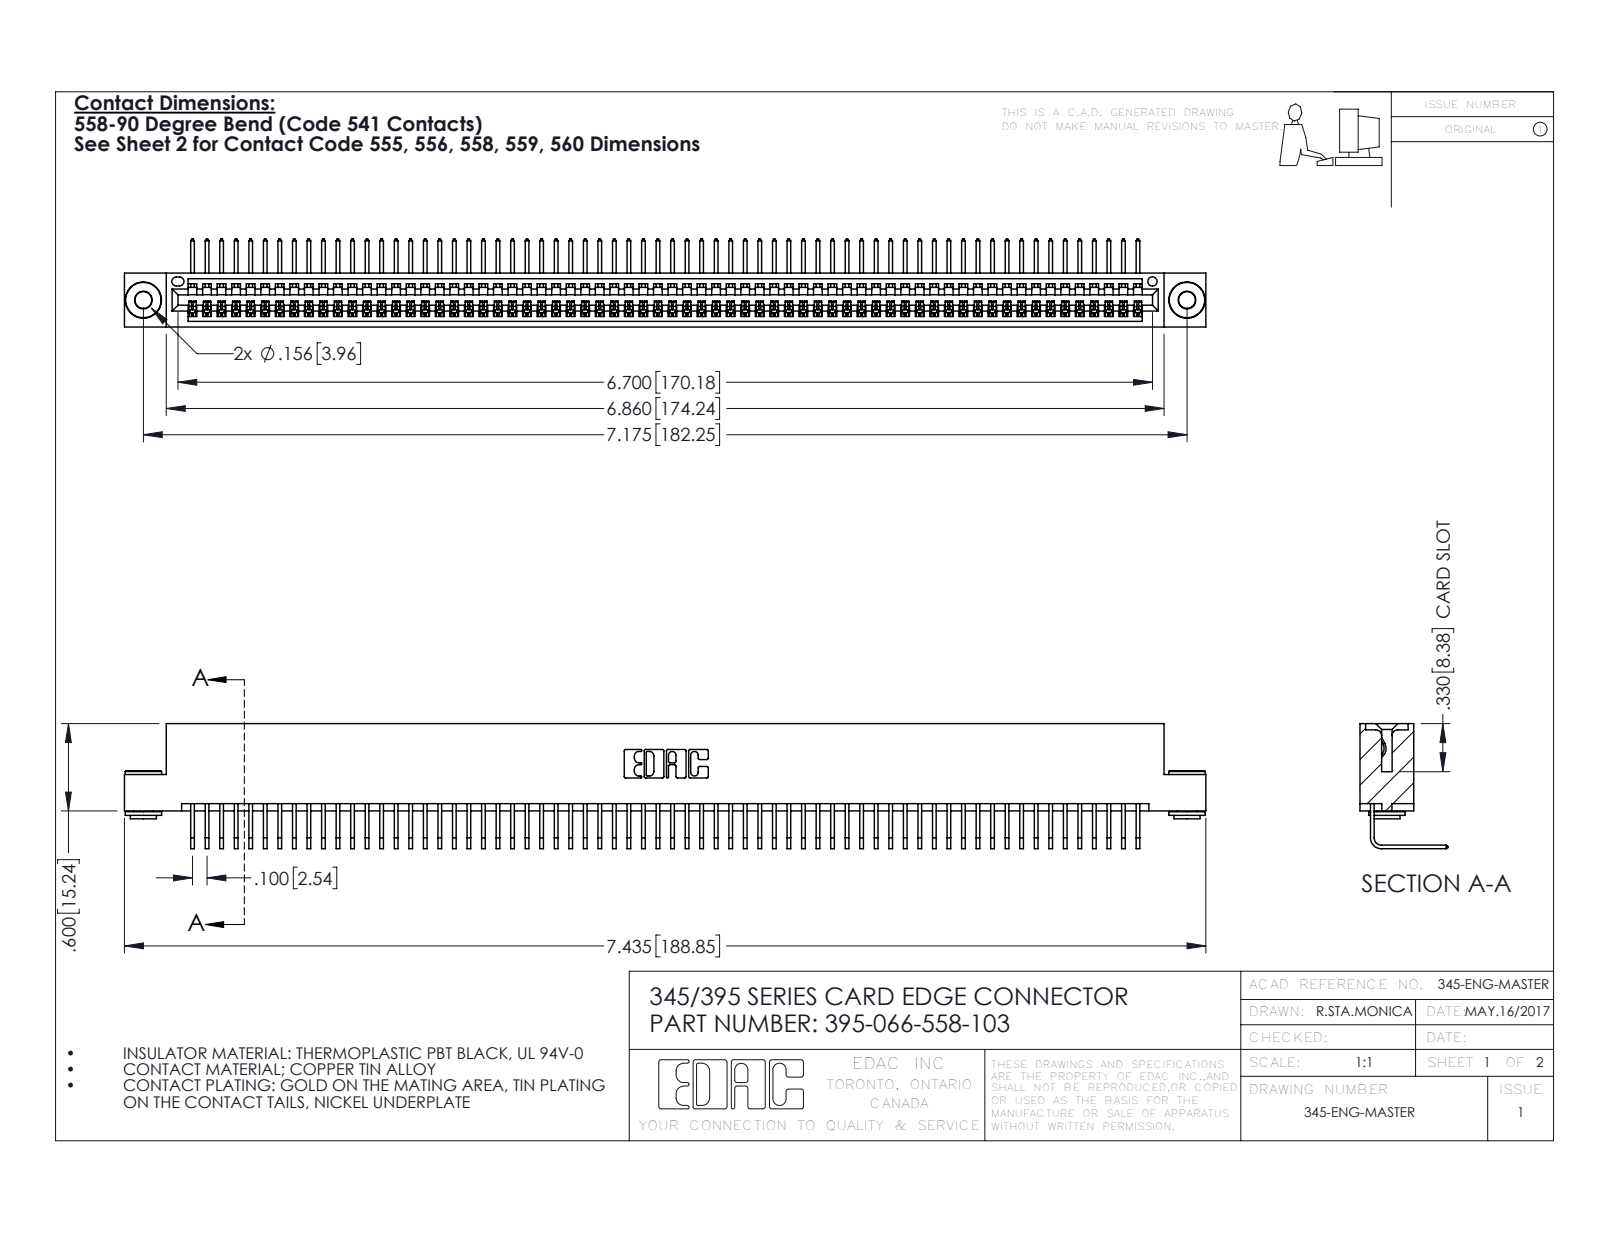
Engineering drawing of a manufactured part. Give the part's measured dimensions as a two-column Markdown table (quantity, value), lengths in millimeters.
| quantity | value |
| --- | --- |
| part name | 345 Part_Flush Mounting Lugs - 0.156 Dia-TH; 345-250-002_345-250-002-102; 345-292-001_558 Tail - 2; 395-066-558-103 |
| STEP written by | SolidWorks 2016 (CONFIG_CONTROL_DESIGN) |
| units | millimeters |
| bodies | 69 solids, 4124 faces (2862 planar, 1254 cylindrical, 8 other) |
| overall size | 188.8 × 21.8 × 15.4 |
| volume | 18 370 mm³ |
| surface area | 26 250 mm² |
| round holes (diameter × count) | 2.9 × 2, 4 × 2, 1.6 × 1 |
| round bosses / shafts (diameter × count) | 6.4 × 2, 4.6 × 2, 3.5 × 2 |
| partial cylindrical surfaces (radius × count) | 0.2 × 132, 0.3 × 22, 0.2 × 6, 0.8 × 6, 0.7 × 3, 0.8 × 2, 1 × 2, 0.4 × 1 |
| main face-to-face distances | 1.8, 7.6, 9.4, 5.1, 0.6, 2.5, 6.9, 5.7, 3.8, 1.8 |
| hole center spacings | 6.9, 176.3, 182.2 |
